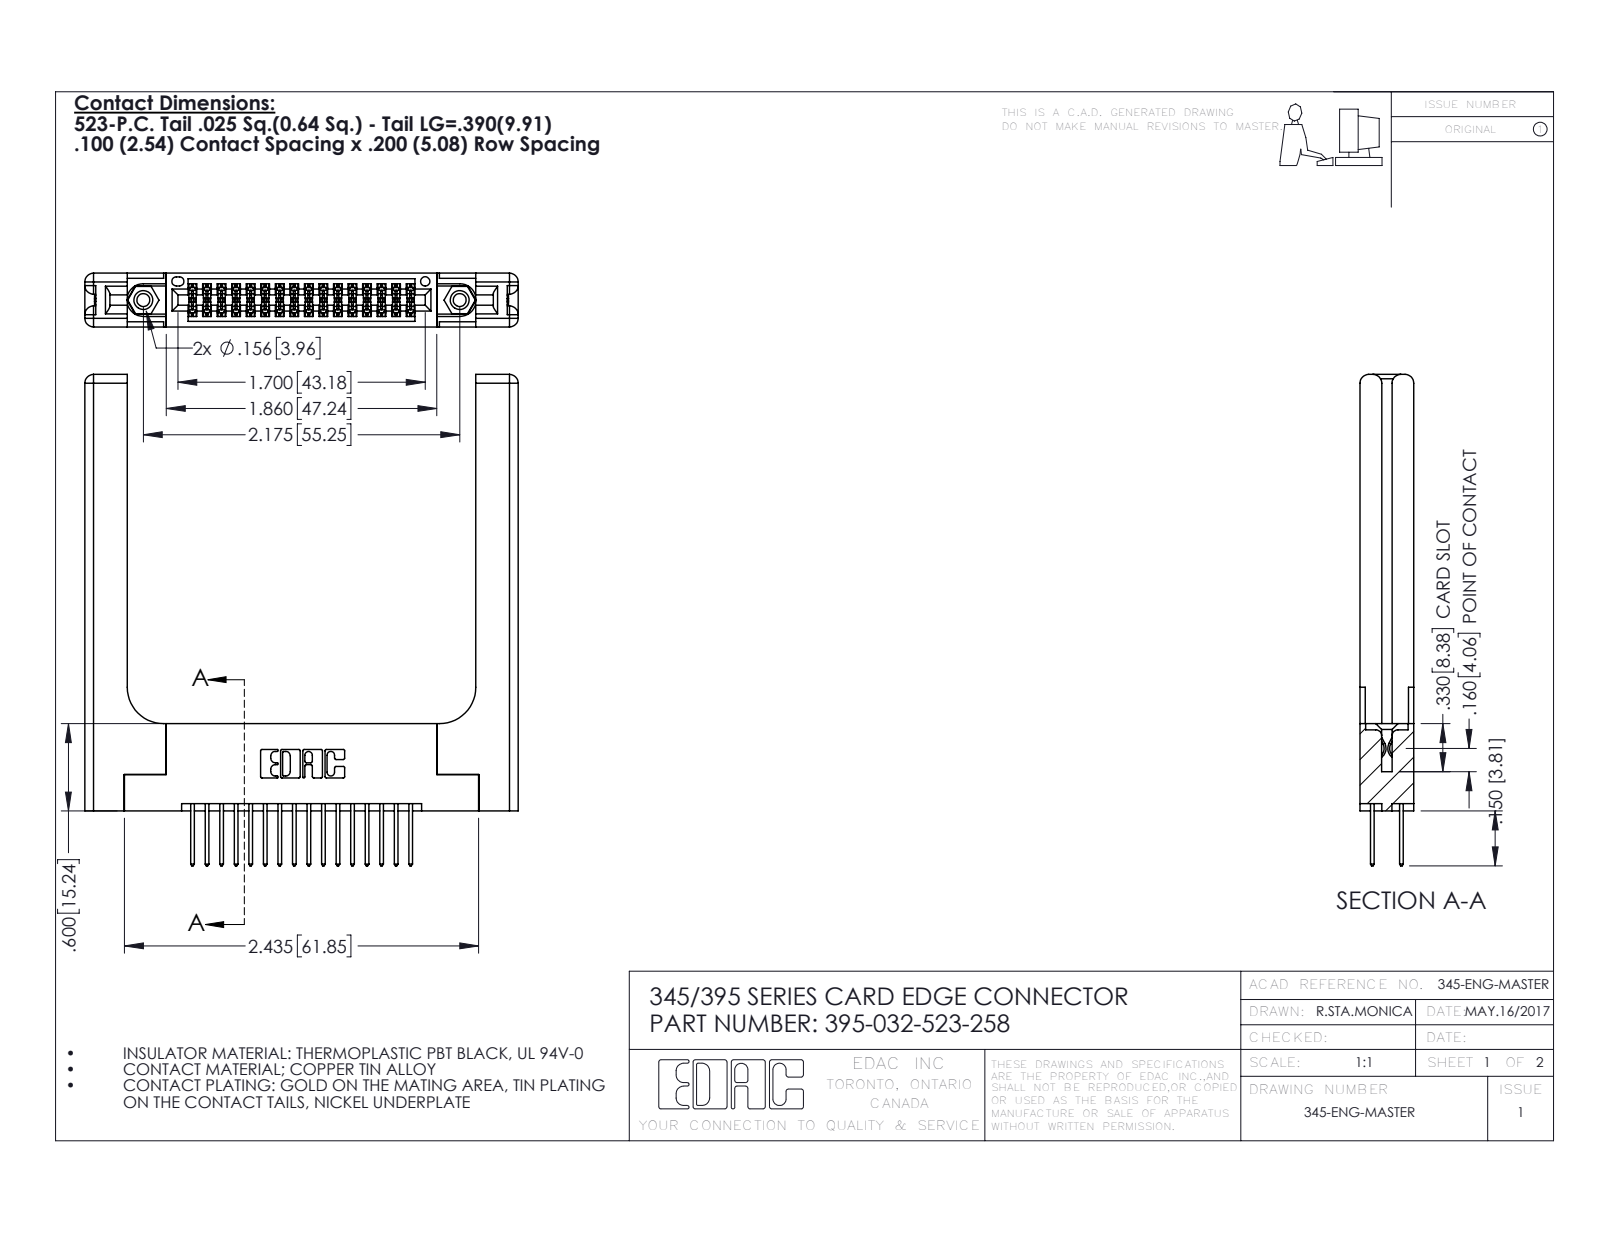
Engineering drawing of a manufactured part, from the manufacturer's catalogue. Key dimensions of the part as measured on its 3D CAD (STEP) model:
Part name (STEP PRODUCT): 345-250-001_345-250-001-102; 345-220-058_345-220-058; 345-292-001_345-293-123; 345 Part_Flush Mounting Lugs - 0.156 Dia-TH (+1 more)
STEP written by: SolidWorks 2016 (CONFIG_CONTROL_DESIGN)
Units: inches
Bodies: 37 solids, 1982 faces (1284 planar, 638 cylindrical, 60 other)
Overall size (bounding box): 3.377 × 2.979 × 0.37
Volume: 0.955 in³ · Surface area: 23.95 in²
Round holes (diameter × count): ⌀0.089 ×2, ⌀0.125 ×2, ⌀0.156 ×2, ⌀0.064 ×1
Round bosses / shafts (diameter × count): ⌀0.155 ×2
Partial cylindrical surfaces — rounded edges, fillets, slot ends (radius × count): R0.006 ×48, R0.01 ×32, R0.01 ×22, R0.06 ×16, R0.007 ×6, R0.031 ×6, R0.026 ×3, R0.014 ×2
Main face-to-face distances: 0.37, 0.072, 0.298, 0.2, 0.077, 0.15, 0.148, 0.098, 0.272, 0.025
Hole centre spacings: 0.27, 1.942, 2.175
